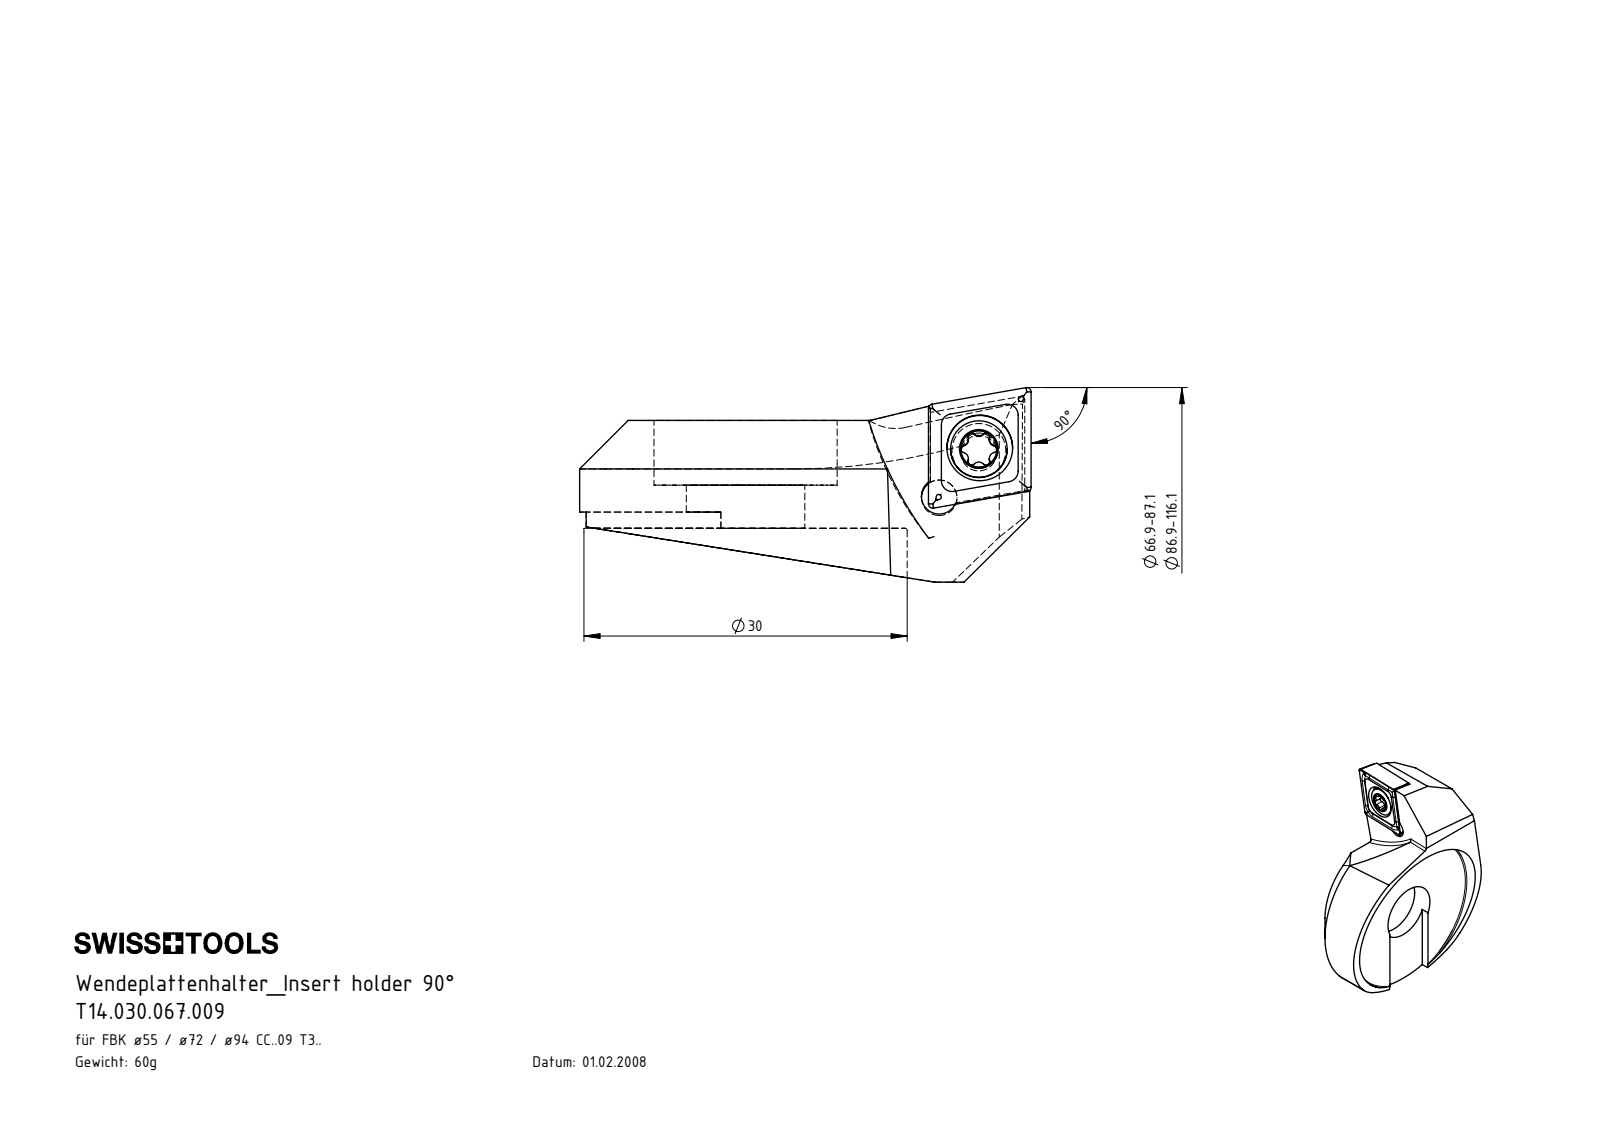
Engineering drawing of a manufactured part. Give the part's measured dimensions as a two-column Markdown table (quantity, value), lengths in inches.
| quantity | value |
| --- | --- |
| part name | F55-WCB.001.013_D_fertigbearbeitet; F55.WCB.001.013; CCMT09T304; WCB-ER2.001.009_A |
| STEP written by | SolidWorks 2017 (AUTOMOTIVE_DESIGN) |
| units | inches |
| bodies | 3 solids, 118 faces (41 planar, 30 cylindrical, 47 other) |
| overall size | 1.65 × 1.303 × 0.711 |
| volume | 0.47 in³ |
| surface area | 6.583 in² |
| round holes (diameter × count) | 0.13 × 2, 0.173 × 1, 0.24 × 1, 0.433 × 1, 0.669 × 1, 1.181 × 1 |
| round bosses / shafts (diameter × count) | 0.207 × 1, 0.157 × 1 |
| partial cylindrical surfaces (radius × count) | 0.013 × 6, 0.023 × 6, 0.02 × 2, 0.394 × 2, 0.197 × 1, 0.652 × 1, 0.823 × 1, 1.181 × 1 |
| main face-to-face distances | 0.394, 0.236, 0.157, 0.335, 0.098, 0.059, 0.148, 0.354, 0.591, 0.256 |
| hole center spacings | 0.226, 0.231 |
